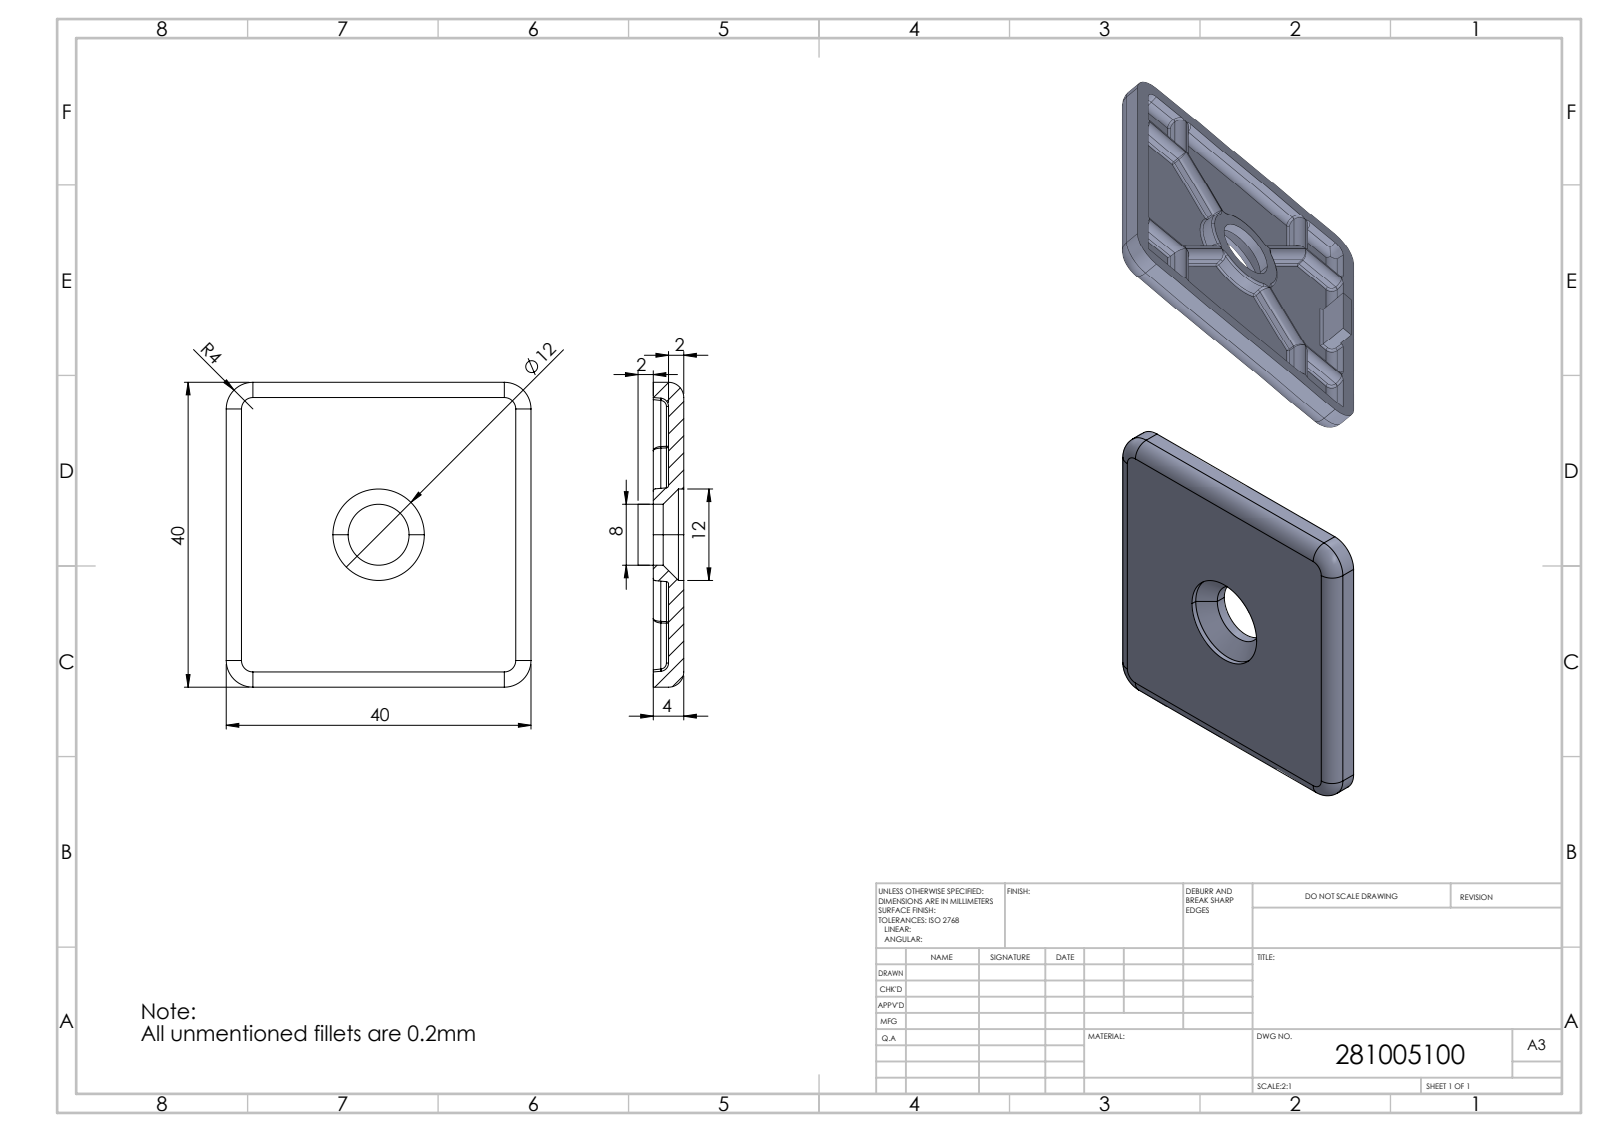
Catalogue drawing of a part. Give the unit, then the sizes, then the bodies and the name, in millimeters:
Units: millimetres
Overall size (bounding box): 40 × 40 × 6
Round holes (diameter × count): ⌀8 ×1, ⌀12 ×1
Partial cylindrical surfaces — rounded edges, fillets, slot ends (radius × count): R0.3 ×41, R1.08 ×20, R2 ×4, R3.5 ×4, R1.5 ×1
Main face-to-face distances: 2, 4, 40, 7.97, 21.91, 29.88, 36, 37.5, 1.5, 2.5
Volume: 4 026 mm³ · Surface area: 4 151 mm²
Bodies: 1 solid, 266 faces (56 planar, 103 cylindrical, 107 other)
Part name (STEP PRODUCT): 281005100_c_1
STEP written by: SolidWorks 2020 (AUTOMOTIVE_DESIGN)
